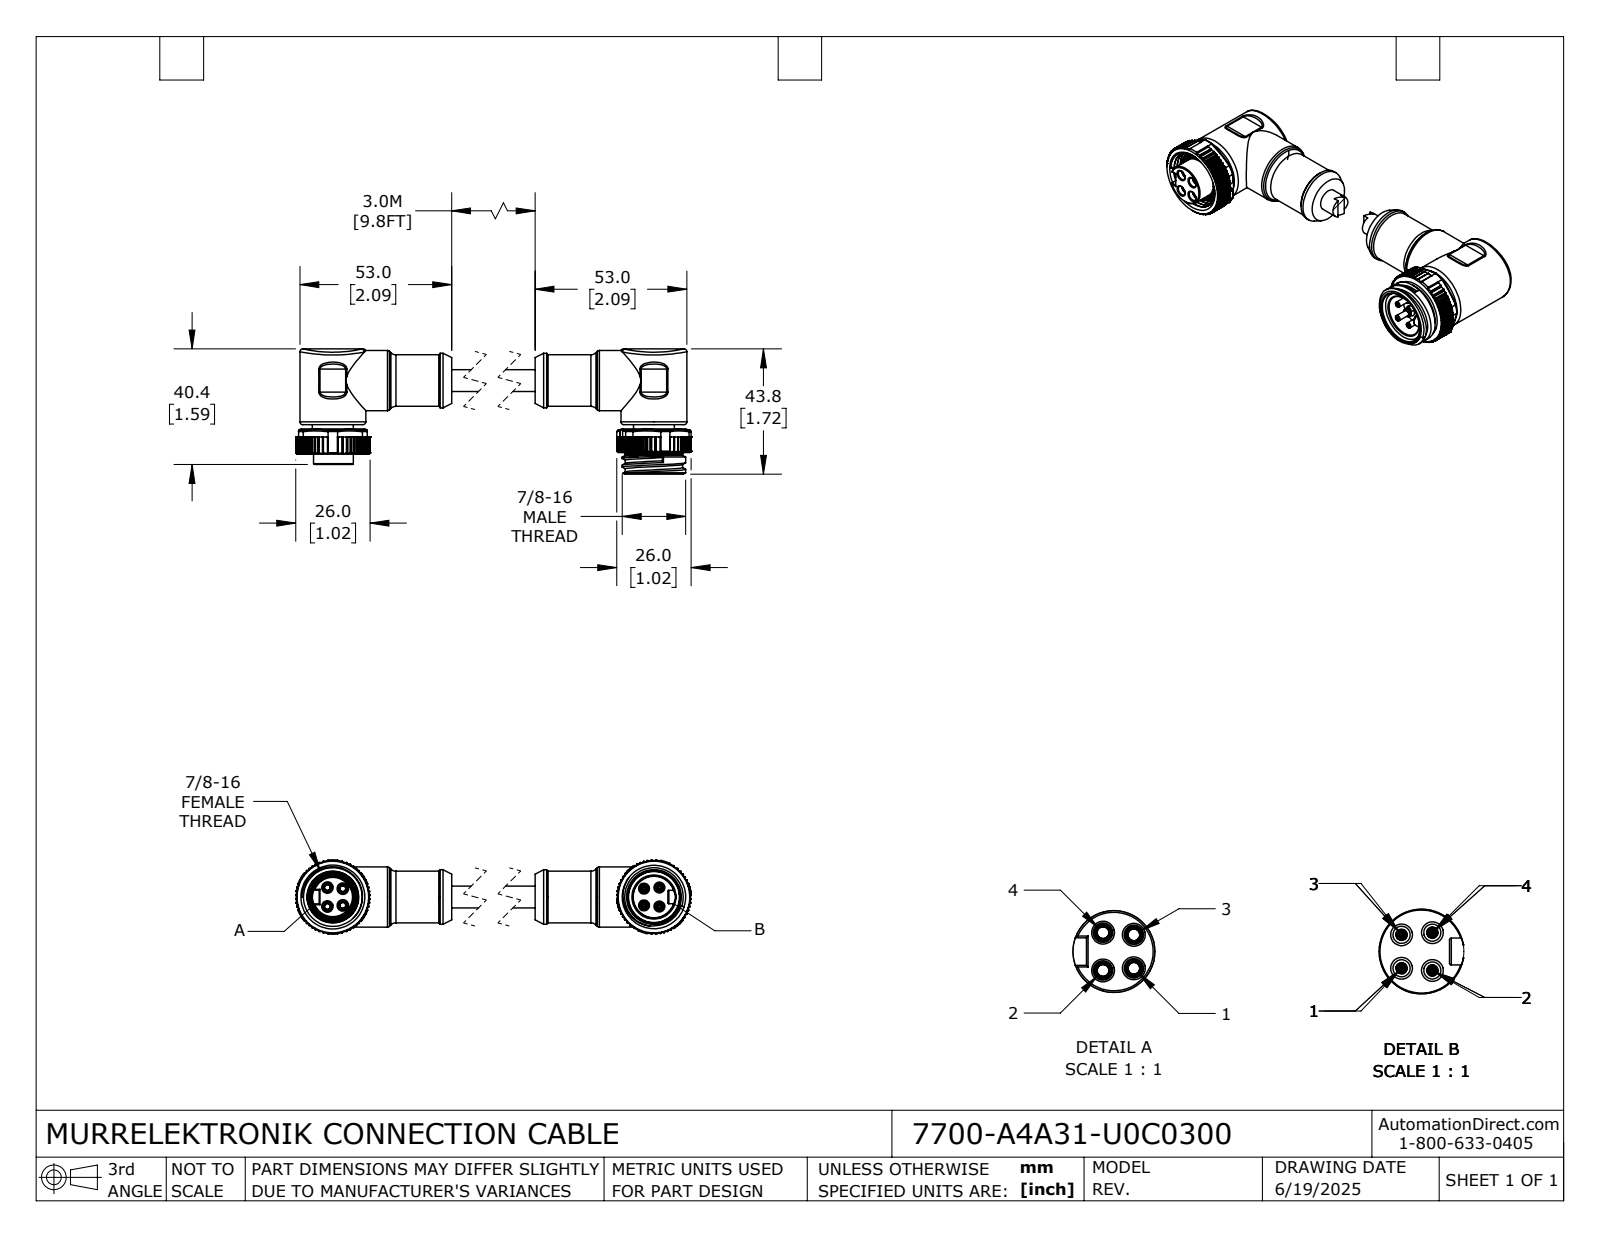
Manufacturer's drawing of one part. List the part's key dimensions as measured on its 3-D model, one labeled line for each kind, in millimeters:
Part name (STEP PRODUCT): 7700-A4A31-U0C0300; 7700-A4A31-U0C0300_MALE; 7700-A4A31-U0C0300_FEMALE
STEP written by: SolidWorks 2024 (CONFIG_CONTROL_DESIGN)
Units: millimetres
Bodies: 2 solids, 1268 faces (520 planar, 581 cylindrical, 167 other)
Overall size (bounding box): 138.97 × 43.76 × 26
Volume: 49 781 mm³ · Surface area: 17 240 mm²
Round holes (diameter × count): ⌀2.05 ×4, ⌀3 ×4, ⌀3.4 ×4, ⌀15.6 ×2, ⌀15.5 ×1, ⌀18.5 ×1, ⌀20.5 ×1, ⌀22.22 ×1
Round bosses / shafts (diameter × count): ⌀3 ×4, ⌀2 ×4, ⌀23 ×2, ⌀18.1 ×2, ⌀17.8 ×2, ⌀14.3 ×2, ⌀22.17 ×1, ⌀21 ×1
Partial cylindrical surfaces — rounded edges, fillets, slot ends (radius × count): R0.2 ×252, R0.3 ×34, R0.1 ×8, R1 ×8, R0.7 ×4, R0.73 ×4, R2.5 ×4, R13 ×2
Main face-to-face distances: 1.5, 8.8, 7.3, 9.7, 0.9, 7, 30, 8.2, 21, 4.2
Hole centre spacings: 3.81, 4.54, 5.39, 8.22, 109.56, 114.95, 5.84, 6.6
